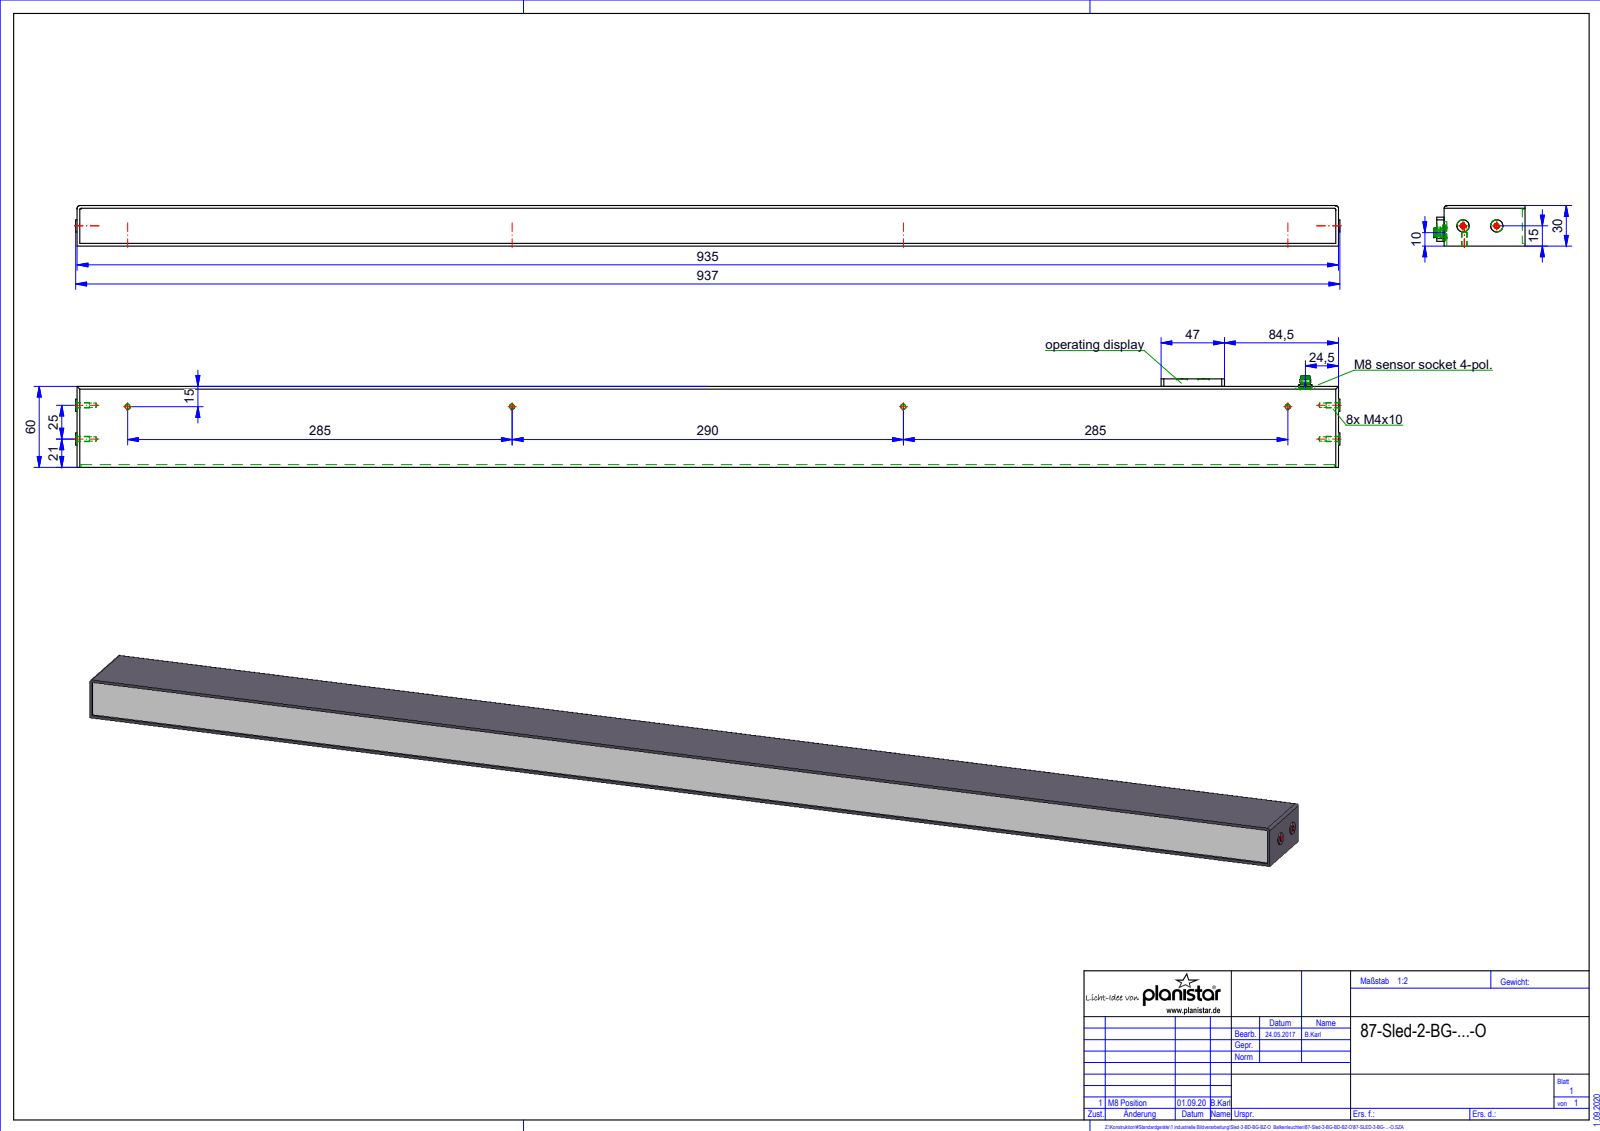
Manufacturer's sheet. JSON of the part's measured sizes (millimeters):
{"part_name": "Root; Baugruppe_Balkenleuchte; QUADER_3; 09-3391-00-04 (+1 more)", "step_written_by": "HiCAD 2015 2002.1 Build 408 (AUTOMOTIVE_DESIGN)", "units": "millimeters", "bodies": {"solids": 3, "faces": 114, "planar": 47, "cylindrical": 50, "other": 17}, "overall_size": [937, 67.7, 30], "volume_mm3": 1637000, "surface_area_mm2": 179445, "round_holes": [[3.3, 6], [4, 6], [5.8, 1]], "round_bosses_or_shafts": [[1, 4], [8, 3], [9, 2], [7.2, 1], [6.8, 1], [6.4, 1]], "partial_cylinders_radius": [[2, 7], [1, 2], [2.5, 2], [5.5, 1]], "face_to_face_distances": [30, 58, 2, 60, 28, 26, 935, 65.5, 63.5, 5.5], "hole_center_spacings": [285, 575, 25, 290, 860]}
